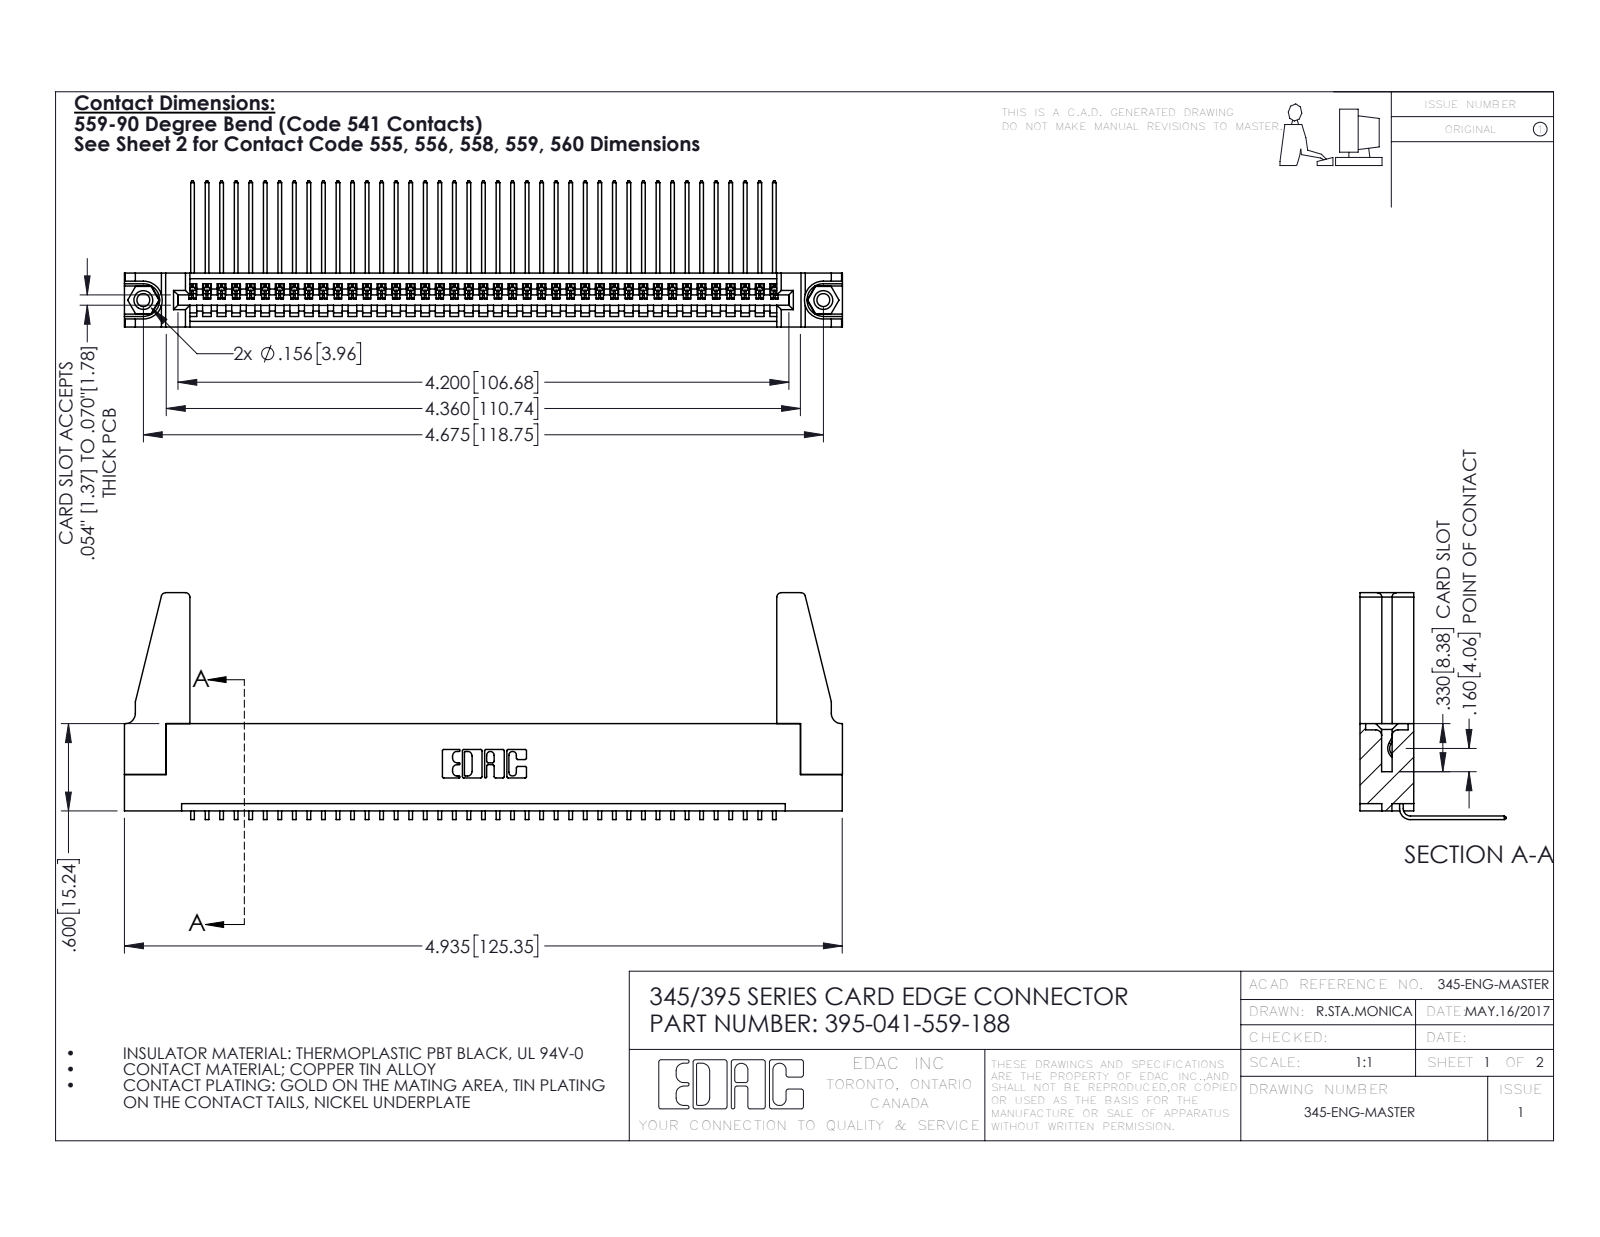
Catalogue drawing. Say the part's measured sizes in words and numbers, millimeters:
The part is named "345-220-078_345-220-088; 395-041-559-188; 345 Part_Flush Mounting Lugs - 0.156 Dia-TH; 345-292-001_558 559 Tail - 1 (+1 more)". Its 3-D file was written by "SolidWorks 2016 (CONFIG_CONTROL_DESIGN)". It is 46 solids with 2710 faces: 1874 planar, 820 cylindrical and 16 other. Overall it measures 125.4 by 39.6 by 25.5 millimeters. Its volume is 15 300 cubic millimeters and its surface area 19 920 square millimeters. Round holes: 2 of diameter 2.3, 2 of diameter 3.2, 2 of diameter 4, 1 of diameter 1.6. Round bosses or shafts: 2 of diameter 3.9. Partial cylindrical surfaces (rounded edges, fillets, slot ends): 82 of radius 0.2, 22 of radius 0.3, 8 of radius 0.8, 6 of radius 0.2, 6 of radius 0.8, 3 of radius 0.7, 2 of radius 0.8, 2 of radius 1. The main face-to-face distances are 1.8, 9.4, 7.6, 5.1, 2.5, 6.9, 0.6, 5.7, 3.8, 1.8. The hole center spacings are 6.9, 112.8, 118.7.
